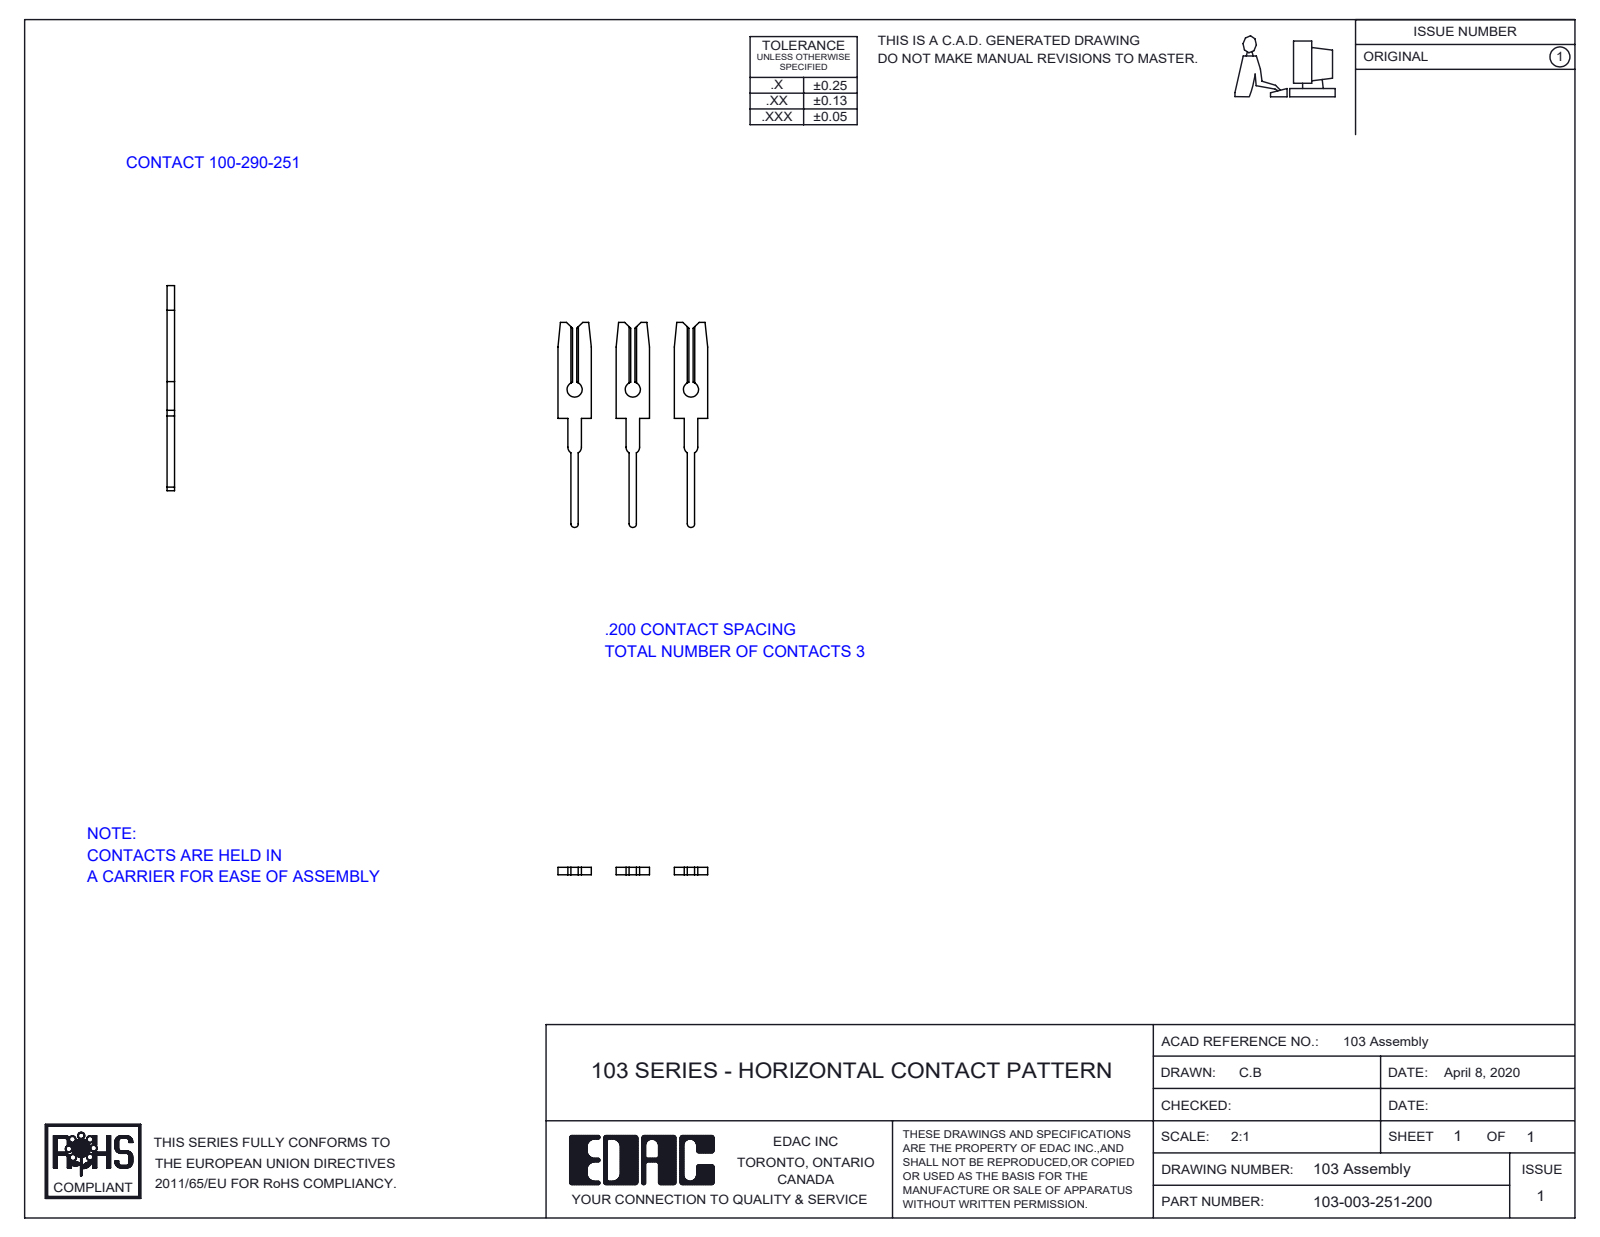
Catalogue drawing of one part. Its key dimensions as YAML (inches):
part_name: "100-290-001_100-290-251; 103-003-251-200"
step_written_by: "SolidWorks 2016 (CONFIG_CONTROL_DESIGN)"
units: inches
bodies: {solids: 3, faces: 84, planar: 66, cylindrical: 18, other: 0}
overall_size: [0.705, 0.515, 0.026]
volume: 0.003
surface_area: 0.418
round_holes:
  - {diameter: 0.052, count: 3}
partial_cylinders:
  - {radius: 0.012, count: 3}
  - {radius: 0.024, count: 3}
face_to_face_distances: [0.026, 0.2, 0.045, 0.07, 0.4, 0.245, 0.27, 0.155, 0.13, 0.115]
hole_center_spacings: [0.2, 0.4]
